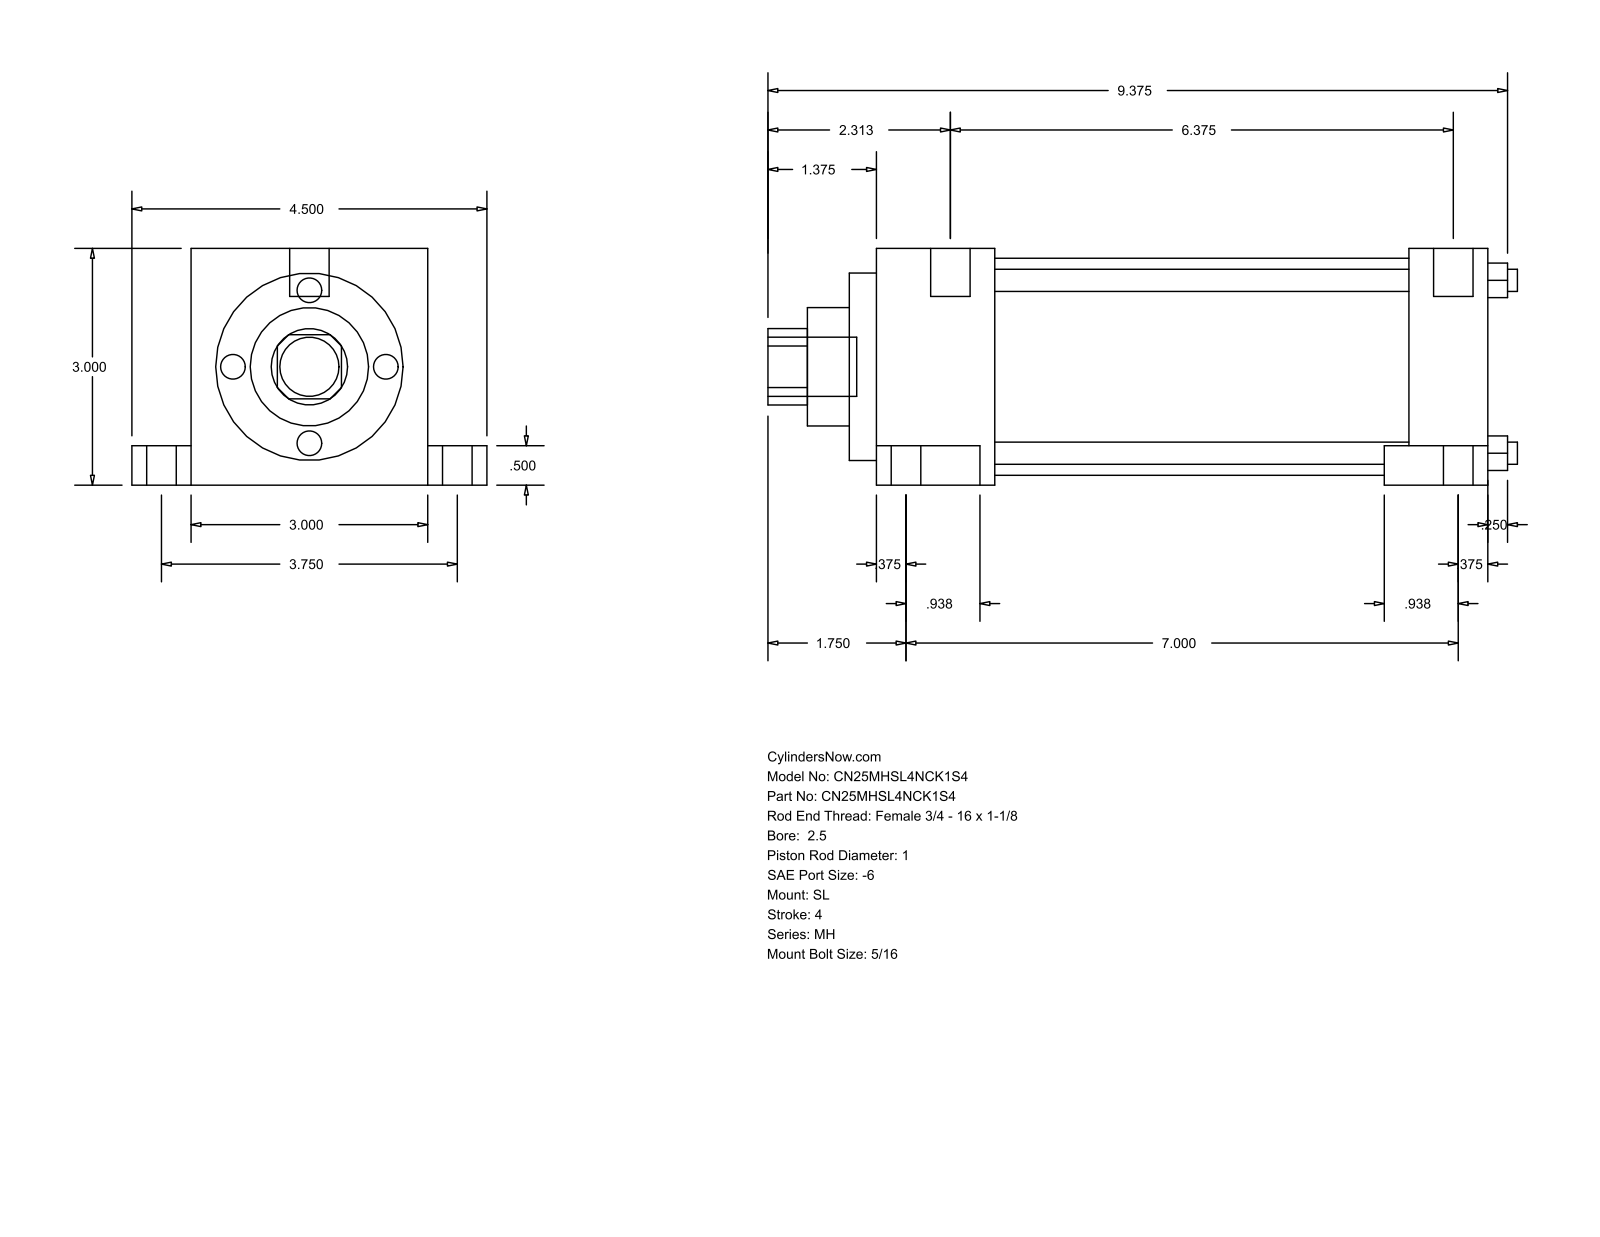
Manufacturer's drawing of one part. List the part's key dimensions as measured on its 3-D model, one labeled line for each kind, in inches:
Part name (STEP PRODUCT): MH_SL__0250_1
STEP written by: GSSL Pune (CONFIG_CONTROL_DESIGN)
Units: inches
Bodies: 0 solids, 86 faces (61 planar, 25 cylindrical, 0 other)
Overall size (bounding box): 9.5 × 4.5 × 3
Round holes (diameter × count): ⌀0.281 ×4, ⌀1 ×1, ⌀1.5 ×1, ⌀2.375 ×1, ⌀2.75 ×1
Round bosses / shafts (diameter × count): ⌀0.625 ×2, ⌀0.375 ×2, ⌀0.219 ×2, ⌀0.75 ×1, ⌀0.5 ×1
Partial cylindrical surfaces — rounded edges, fillets, slot ends (radius × count): R0.484 ×1
Main face-to-face distances: 3, 1, 7.094, 8.094, 0.5, 2.5, 0.75, 3.75, 0.531, 7.625
Hole centre spacings: 1.548, 2.19, 3.097
